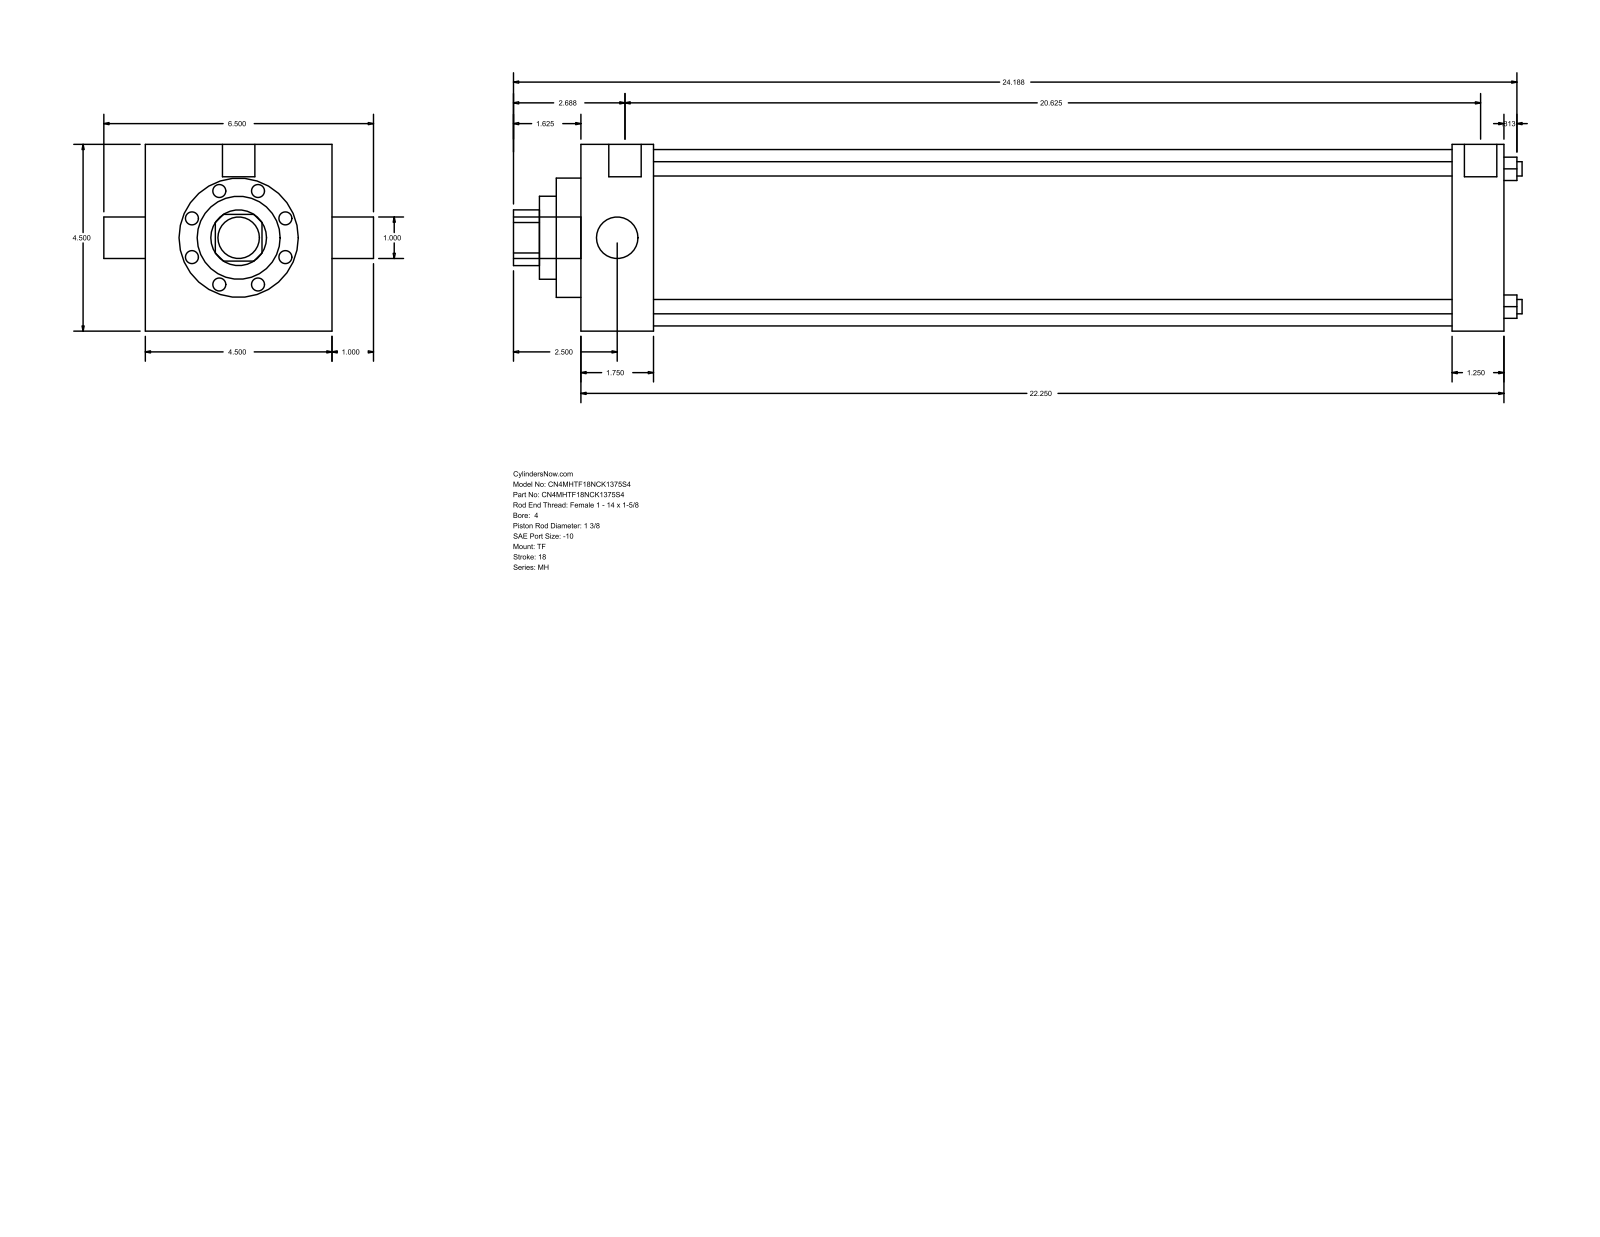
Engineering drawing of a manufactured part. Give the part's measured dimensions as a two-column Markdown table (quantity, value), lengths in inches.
| quantity | value |
| --- | --- |
| part name | MH_TF__0400_1.375 |
| STEP written by | GSSL Pune (CONFIG_CONTROL_DESIGN) |
| units | inches |
| bodies | 0 solids, 86 faces (61 planar, 25 cylindrical, 0 other) |
| overall size | 24.313 × 6.5 × 4.5 |
| round holes (diameter × count) | 0.345 × 4, 1 × 1, 1.375 × 1, 2 × 1, 2.875 × 1, 4.25 × 1 |
| round bosses / shafts (diameter × count) | 0.344 × 3, 0.781 × 2, 1 × 1 |
| partial cylindrical surfaces (radius × count) | 0.672 × 1 |
| main face-to-face distances | 4.5, 22.25, 1.75, 20.5, 21, 19.25, 1.25, 0.594, 2.344, 21.594 |
| hole center spacings | 2.347, 3.32, 4.695 |
